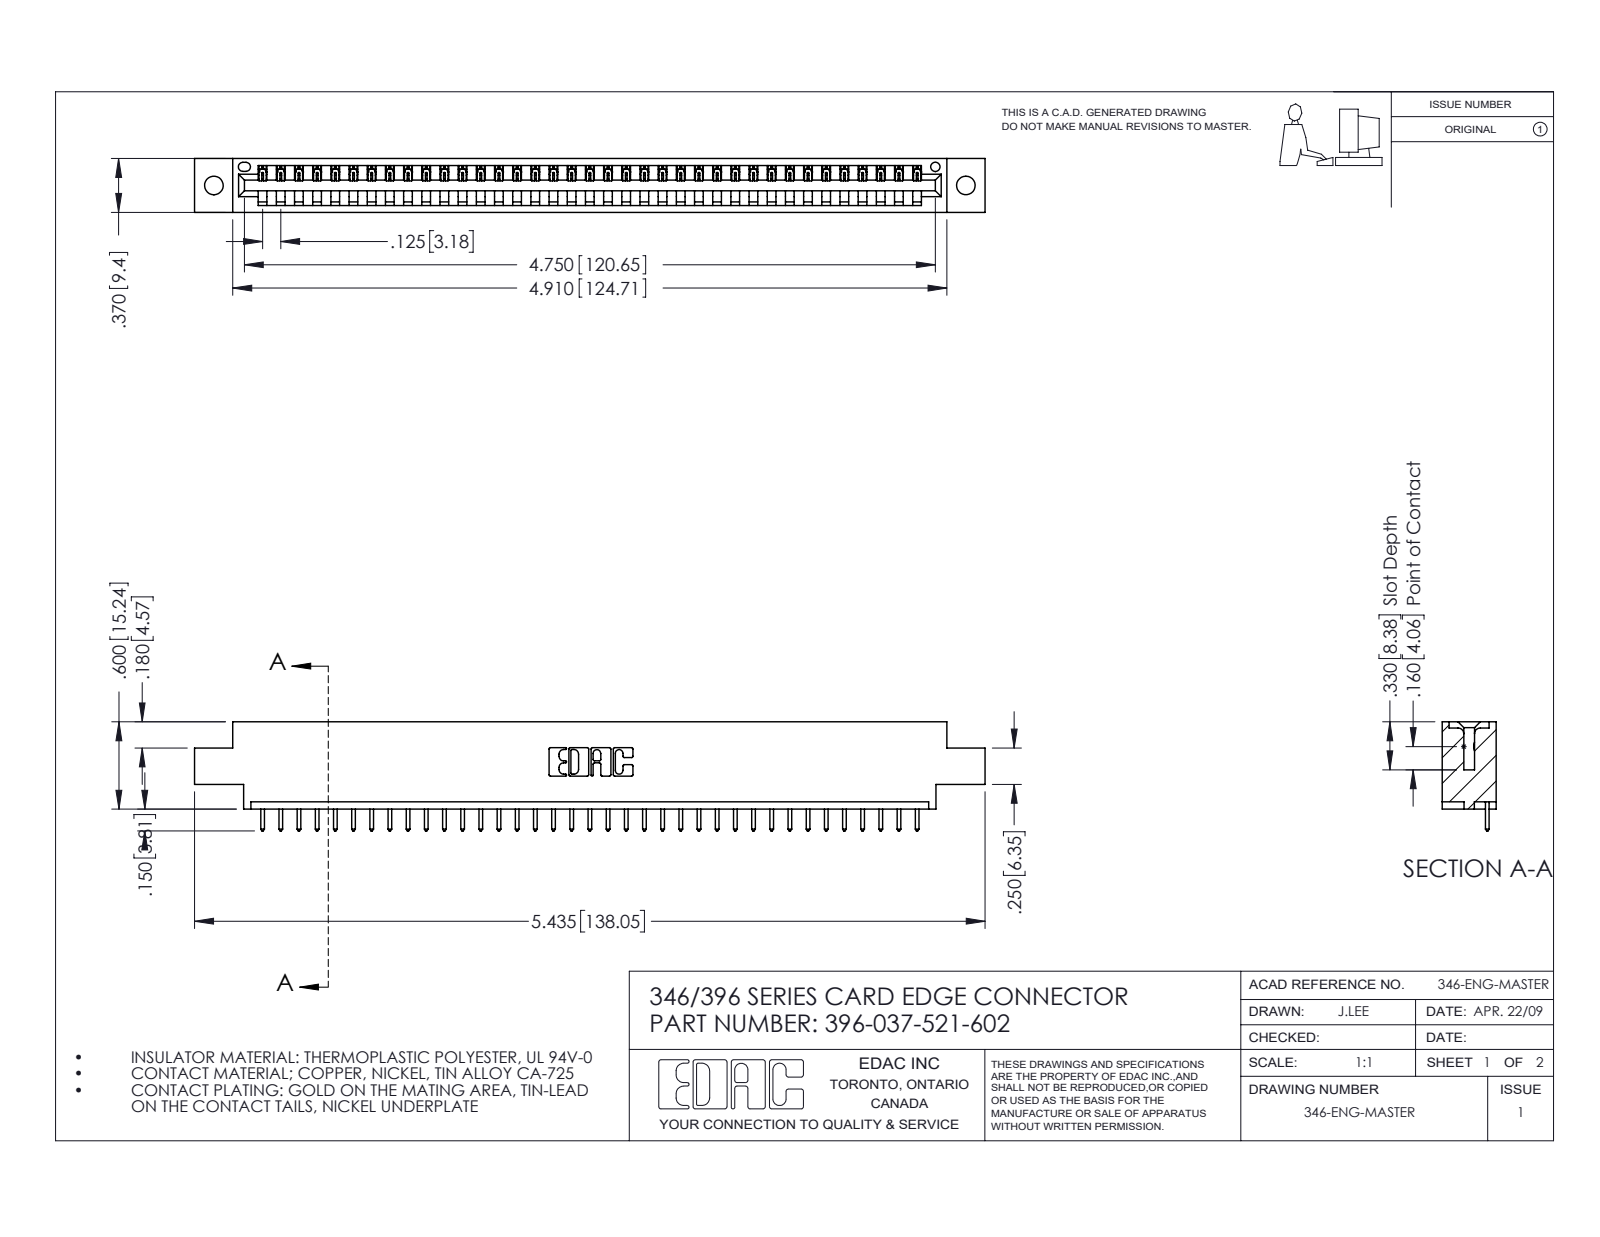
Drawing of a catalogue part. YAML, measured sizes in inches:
part_name: "345-292-001_345-293-121; 346 Part_0.170 Offset - 0.128 Dia; 396-037-521-602"
step_written_by: "SolidWorks 2016 (CONFIG_CONTROL_DESIGN)"
units: inches
bodies: {solids: 38, faces: 2272, planar: 1560, cylindrical: 712, other: 0}
overall_size: [5.435, 0.75, 0.37]
volume: 0.786
surface_area: 24.05
round_holes:
  - {diameter: 0.128, count: 2}
  - {diameter: 0.064, count: 1}
partial_cylinders:
  - {radius: 0.006, count: 74}
  - {radius: 0.01, count: 74}
  - {radius: 0.01, count: 22}
  - {radius: 0.007, count: 6}
  - {radius: 0.031, count: 6}
  - {radius: 0.026, count: 3}
  - {radius: 0.031, count: 2}
  - {radius: 0.04, count: 2}
face_to_face_distances: [0.048, 0.322, 0.37, 0.25, 0.072, 0.298, 0.025, 0.148, 0.222, 0.1]
hole_center_spacings: [0.246, 4.961, 5.17]
